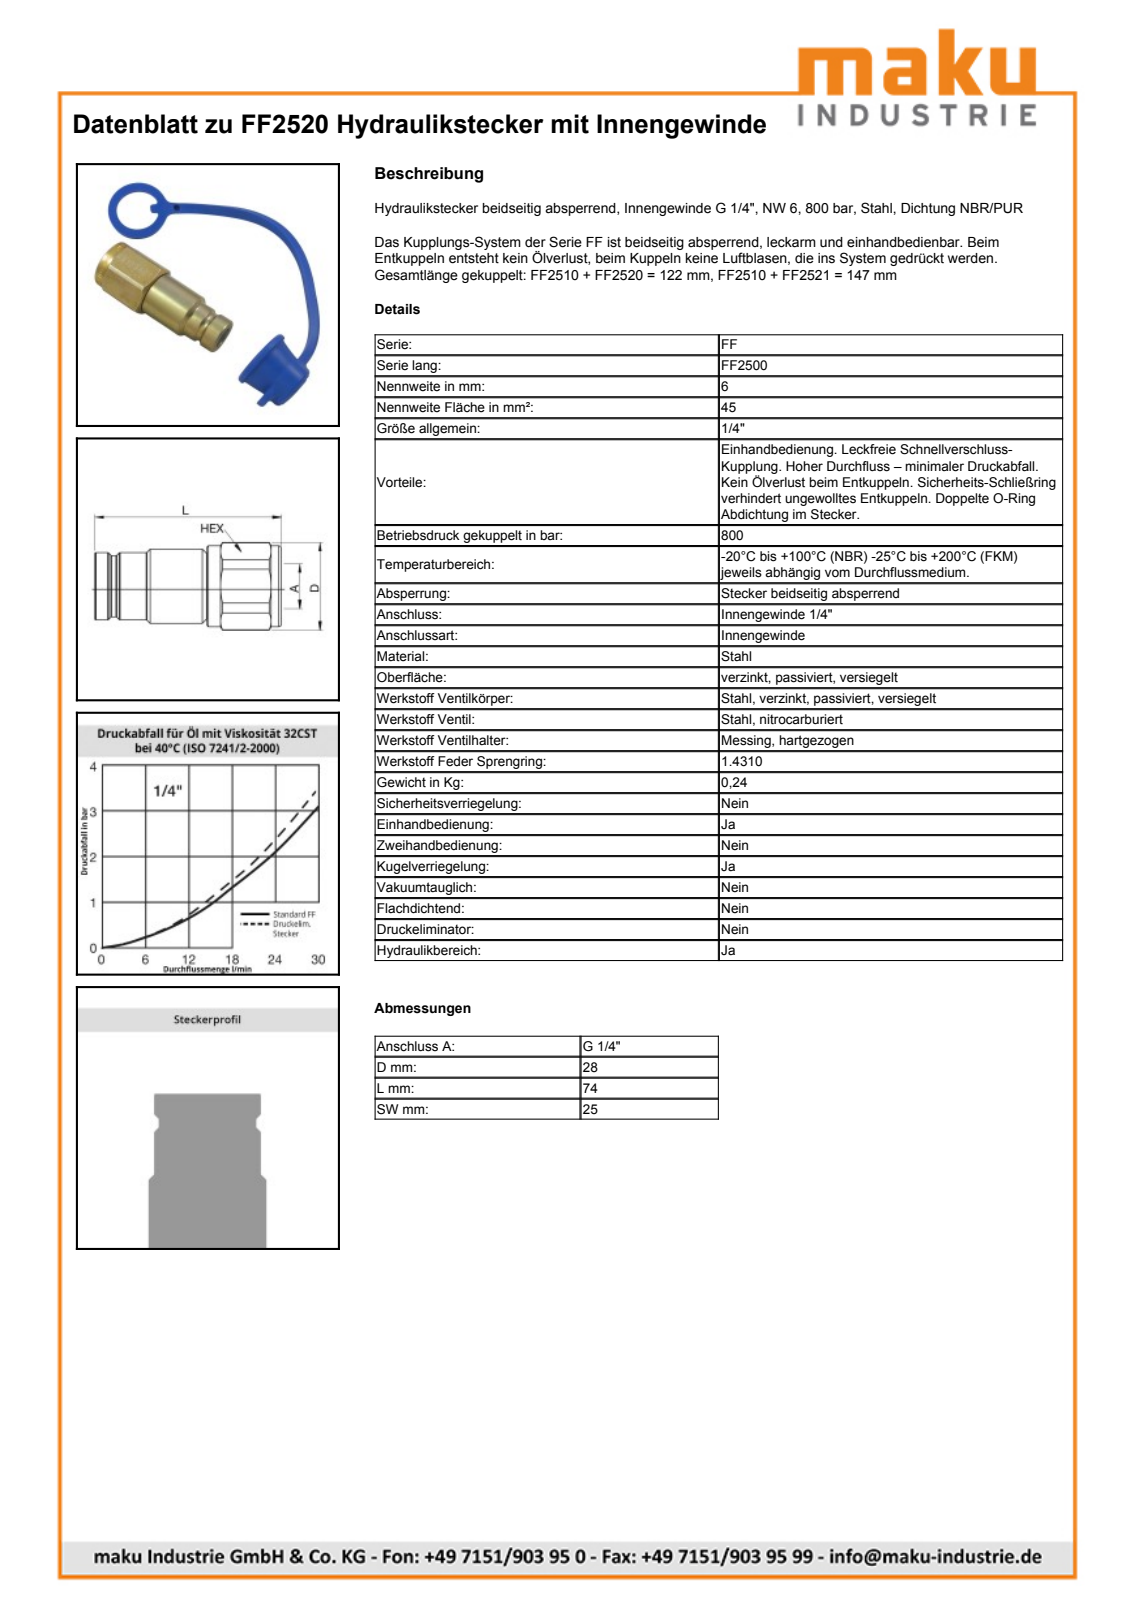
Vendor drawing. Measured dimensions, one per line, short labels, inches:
name: FF2520
written by: SolidWorks 2009 (AUTOMOTIVE_DESIGN)
unit: in
bodies: 1 solid, 614 faces (210 planar, 84 cylindrical, 320 other)
size: 2.913 × 1.181 × 1.063
volume: 2.029 in³; area: 11.4 in²
holes: 1× ⌀0.429, 1× ⌀0.45
bosses: 1× ⌀1.055, 1× ⌀0.925, 1× ⌀0.866, 1× ⌀0.756, 1× ⌀0.65
rounds: 1× R0.527, 1× R0.591
face distances: 1.063, 2.913, 1.213, 1.701, 0.525, 0.687, 2.388, 2.912, 2.387, 1.699
